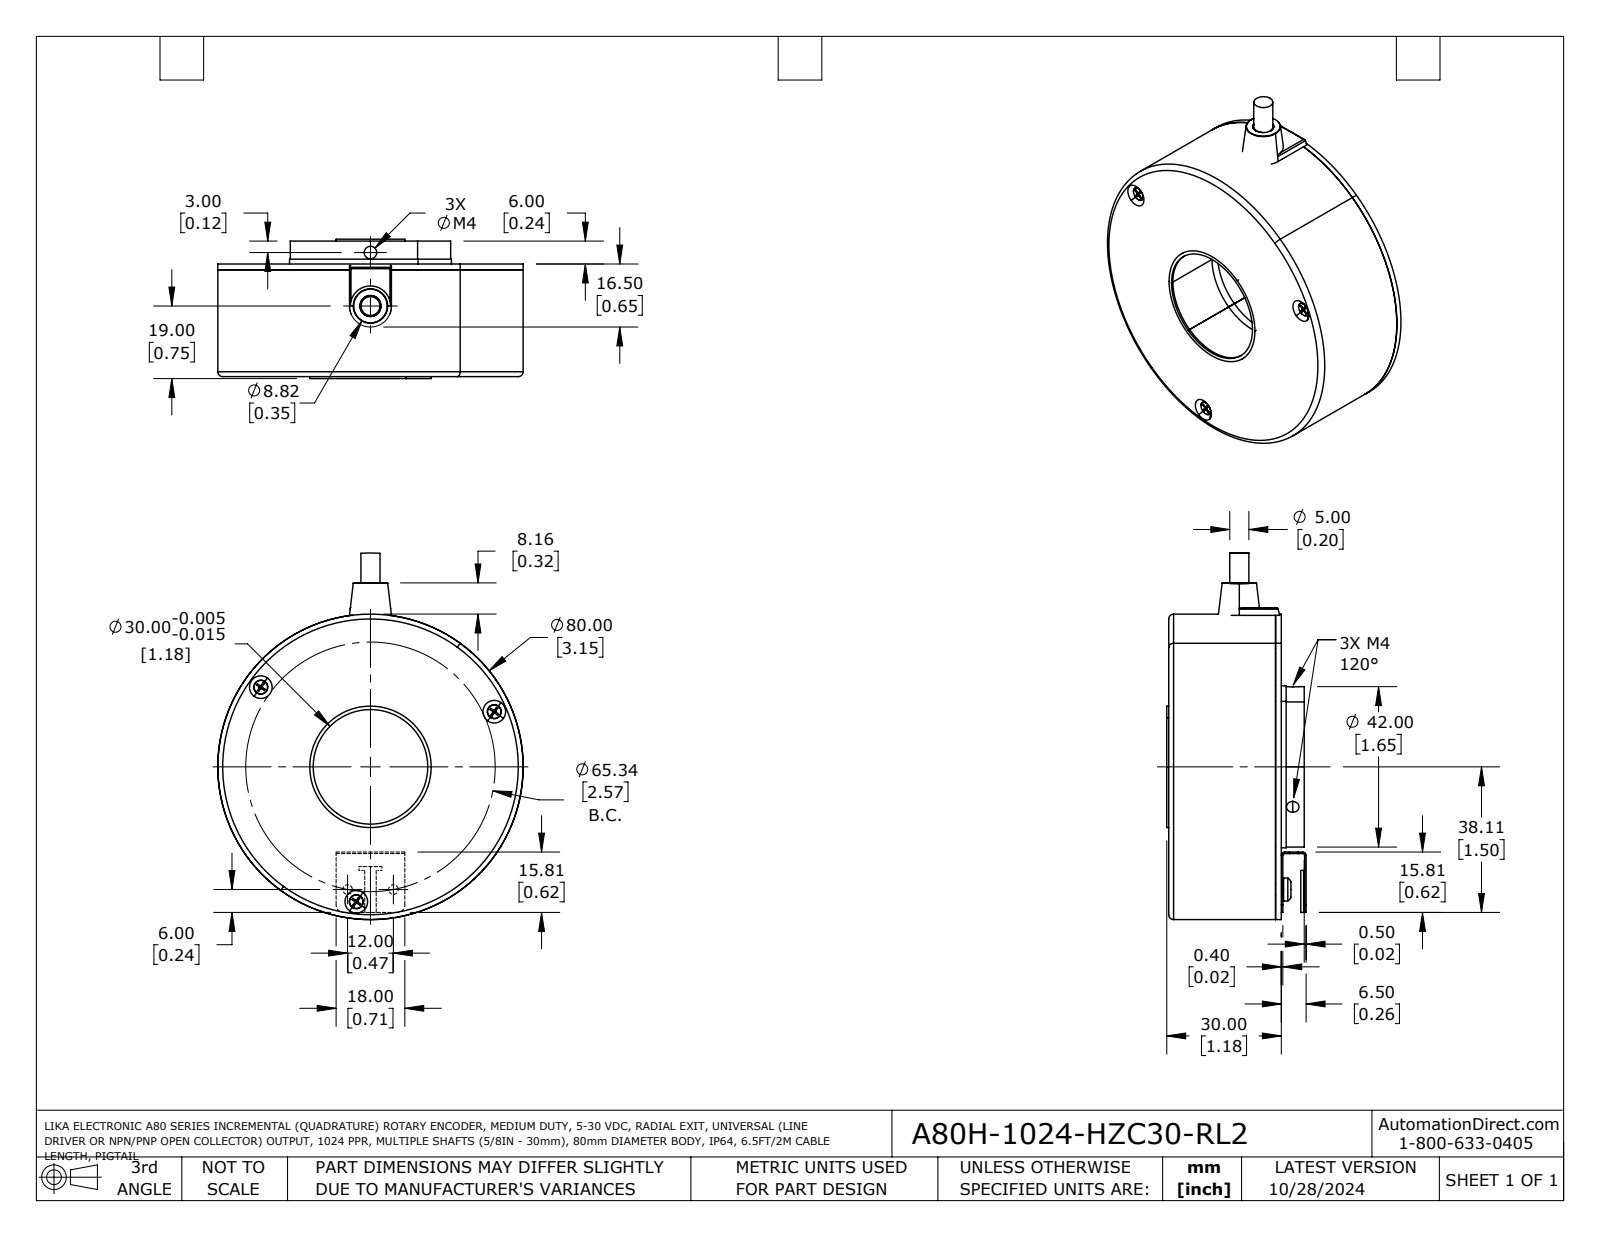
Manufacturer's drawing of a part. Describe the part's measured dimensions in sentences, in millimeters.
The part is named "A80H-1024-HZC30-RL2". Its 3-D file was written by "SolidWorks 2021 (AUTOMOTIVE_DESIGN)". It is 10 solids with 555 faces: 153 planar, 159 cylindrical and 243 other. Overall it measures 96 by 80 by 36.5 millimeters. Its volume is 181 900 cubic millimeters and its surface area 49 030 square millimeters. Round holes: 5 of diameter 3.4, 3 of diameter 3.3, 2 of diameter 2.8, 2 of diameter 4, 1 of diameter 5.6, 1 of diameter 30, 1 of diameter 80. Round bosses or shafts: 3 of diameter 2, 2 of diameter 6, 2 of diameter 3, 1 of diameter 42.4, 1 of diameter 42, 1 of diameter 31.8. Partial cylindrical surfaces (rounded edges, fillets, slot ends): 14 of radius 0.3, 12 of radius 0.4, 9 of radius 0.2, 9 of radius 1, 7 of radius 0.1, 3 of radius 0.2, 3 of radius 0.4, 2 of radius 0.5. The main face-to-face distances are 1.5, 29.5, 28, 15, 13.5, 14.5, 12, 3, 26.5, 9. The hole center spacings are 32.7, 35.5, 61.5, 3.9, 10.2, 12, 14, 35.5.
